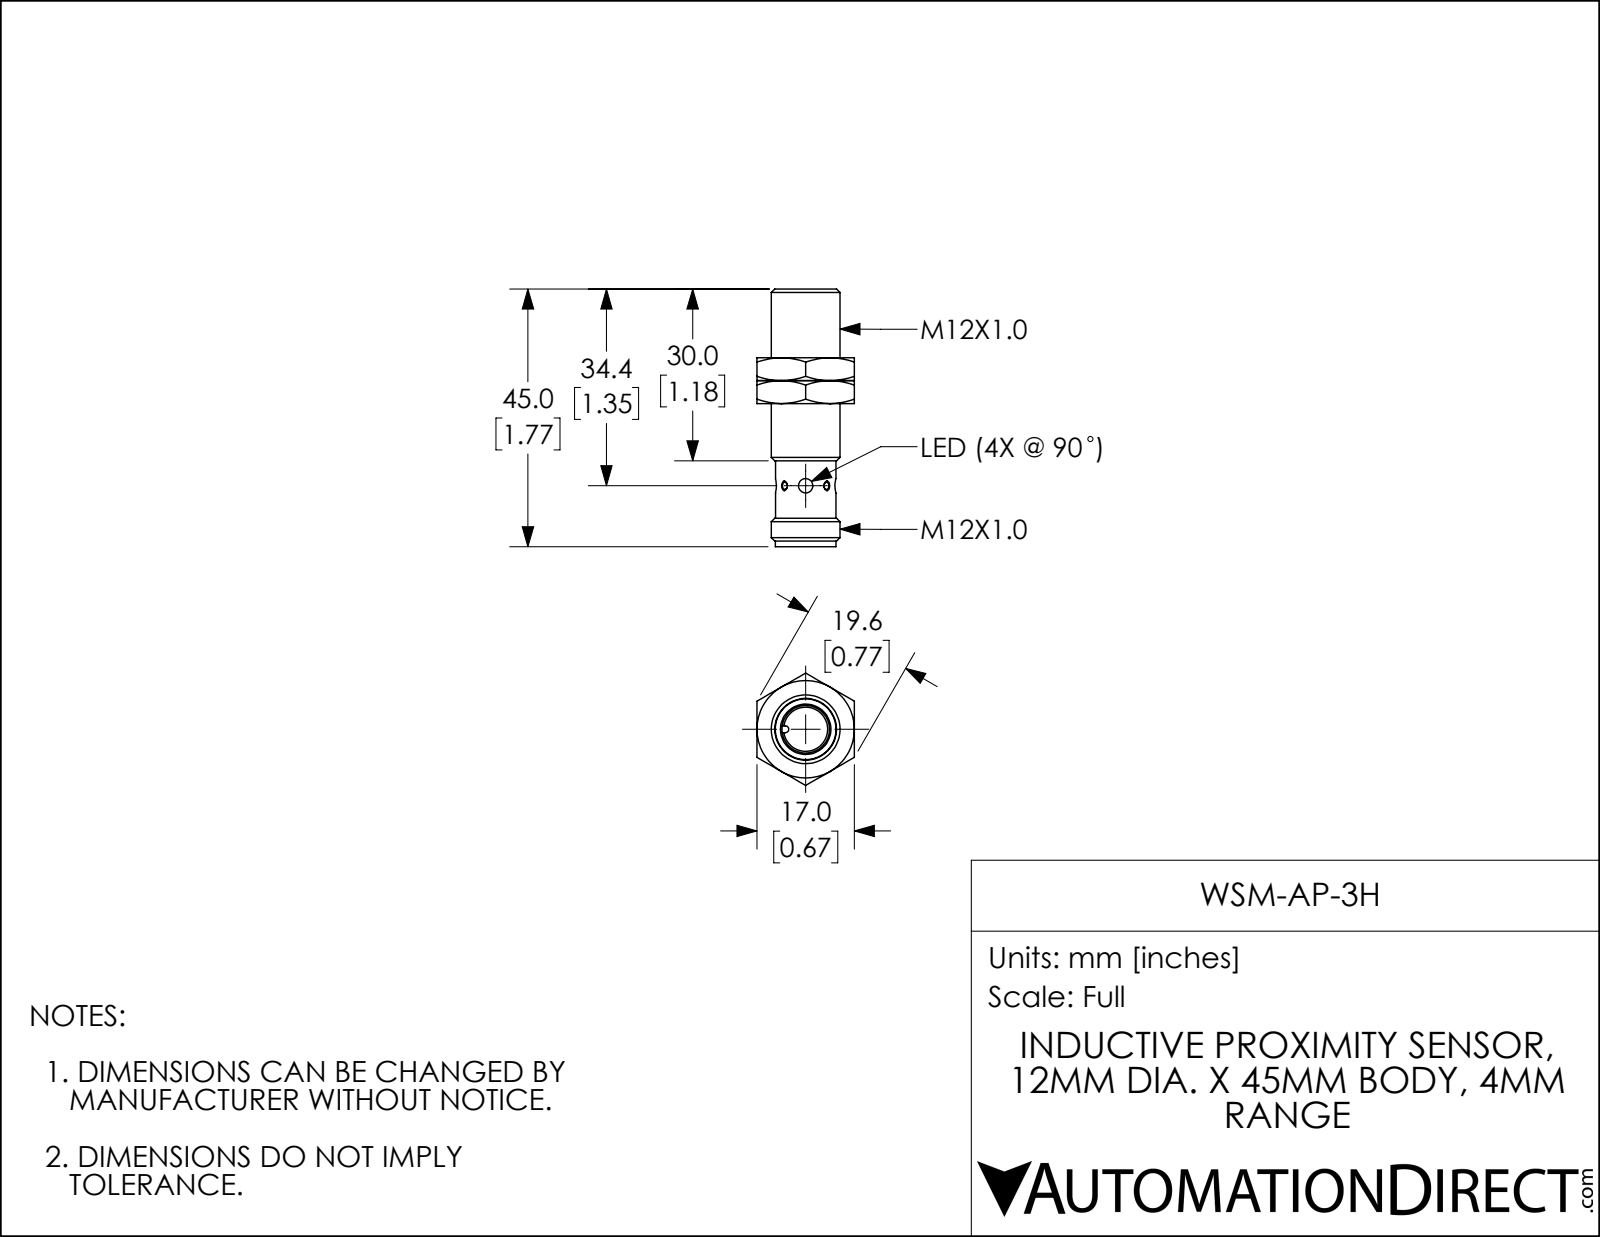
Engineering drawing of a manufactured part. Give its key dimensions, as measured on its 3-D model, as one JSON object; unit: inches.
{"part_name": "WSM-AP-3H", "step_written_by": "SolidWorks 2017 (AUTOMOTIVE_DESIGN)", "units": "inches", "bodies": {"solids": 3, "faces": 88, "planar": 27, "cylindrical": 14, "other": 47}, "overall_size": [1.772, 0.773, 0.669], "volume_in3": 0.336, "surface_area_in2": 5.342, "round_holes": [[0.098, 2], [0.327, 1], [0.402, 1], [0.43, 1]], "round_bosses_or_shafts": [[0.472, 1], [0.417, 1], [0.415, 1], [0.4, 1]], "partial_cylinders_radius": [[0.024, 1]], "face_to_face_distances": [0.157, 0.669, 0.315, 0.787, 0.63, 0.472, 0.634, 0.791, 0.949, 1.421]}
